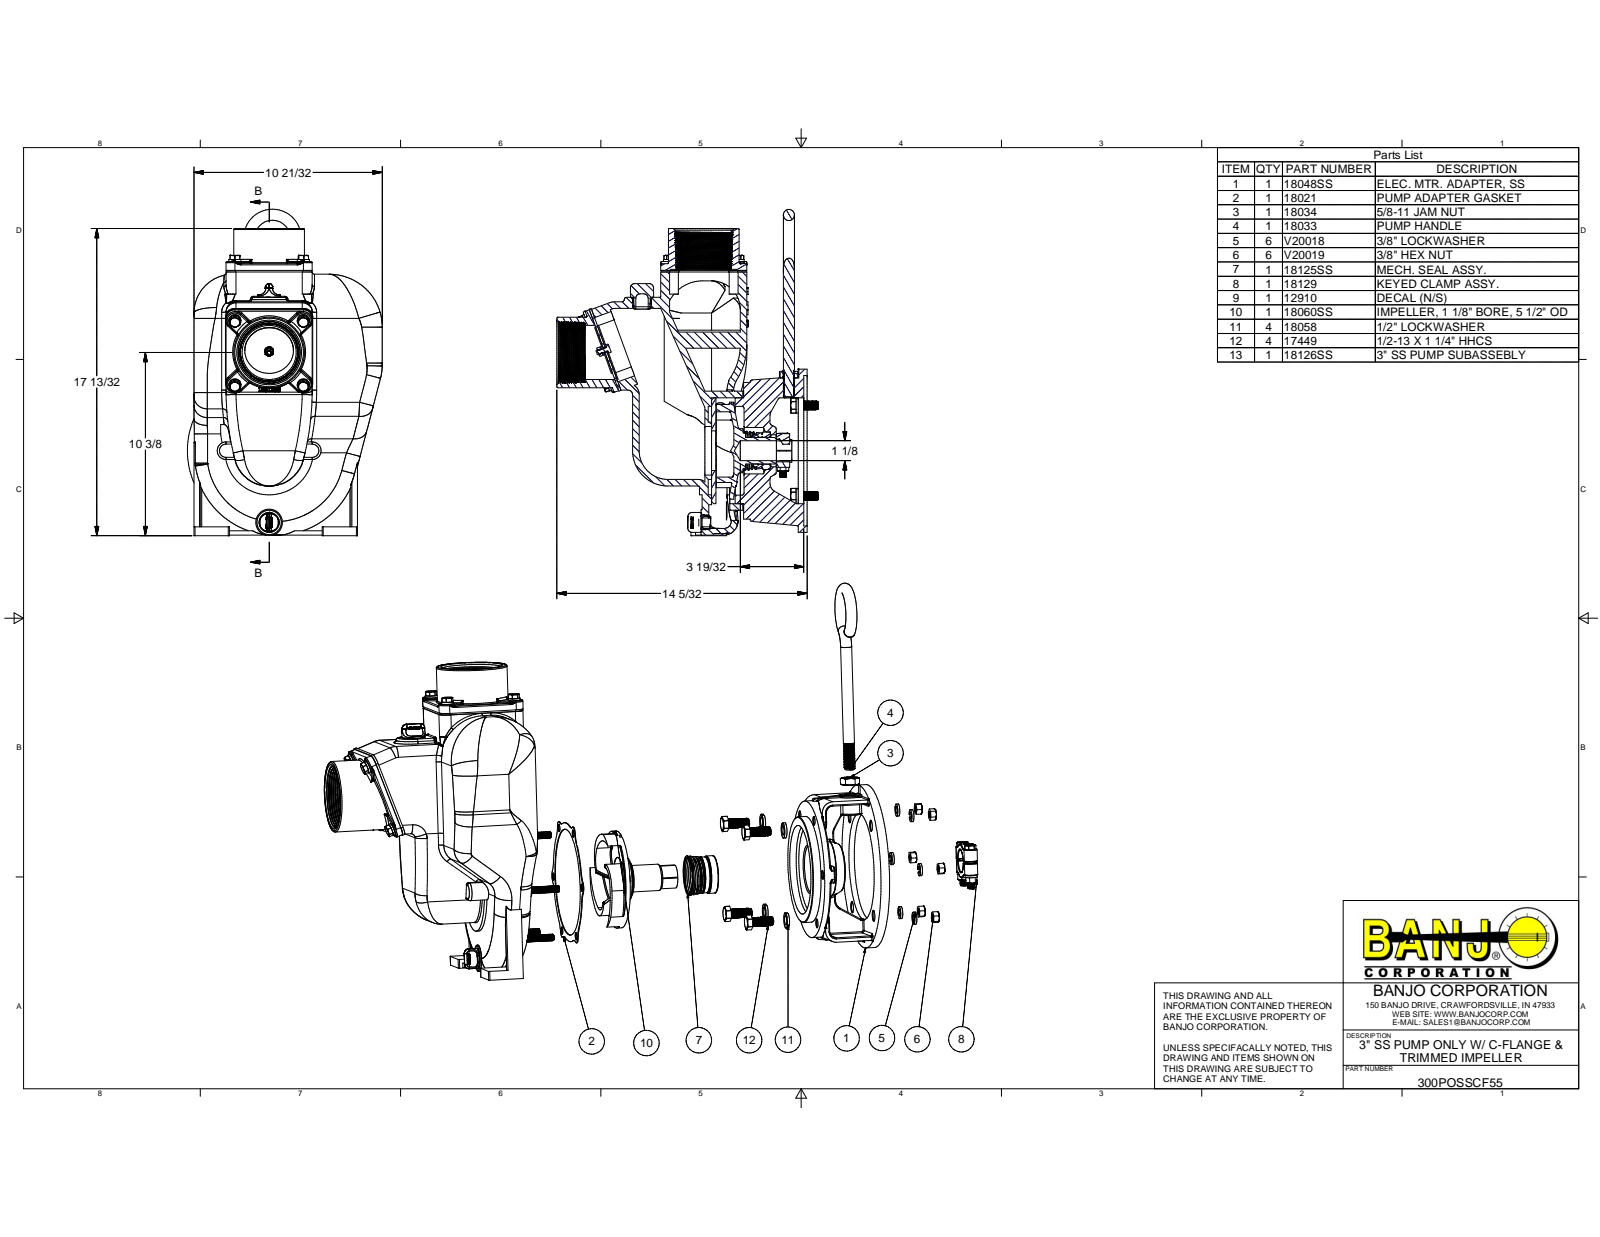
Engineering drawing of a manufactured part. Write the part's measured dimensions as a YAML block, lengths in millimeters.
part_name: "18001SS; 18004SS; 18106SS; V20018 (+8 more)"
step_written_by: "Autodesk Inventor 2014 (AUTOMOTIVE_DESIGN)"
units: millimeters
bodies: {solids: 73, faces: 6779, planar: 1336, cylindrical: 2286, other: 3157}
overall_size: [469.84, 375.46, 280.04]
volume: 5021000
surface_area: 1361000
round_holes:
  - {diameter: 10.32, count: 22}
  - {diameter: 7.8, count: 16}
  - {diameter: 9.78, count: 16}
  - {diameter: 7.81, count: 8}
  - {diameter: 9.52, count: 6}
  - {diameter: 11.11, count: 6}
  - {diameter: 13, count: 4}
  - {diameter: 14.29, count: 4}
  - {diameter: 13.92, count: 3}
  - {diameter: 7.14, count: 2}
  - {diameter: 12.7, count: 2}
  - {diameter: 4.98, count: 1}
round_bosses_or_shafts:
  - {diameter: 8.24, count: 196}
  - {diameter: 11.07, count: 60}
  - {diameter: 17.46, count: 16}
  - {diameter: 9.52, count: 12}
  - {diameter: 5.39, count: 12}
  - {diameter: 7.63, count: 6}
  - {diameter: 22.07, count: 4}
  - {diameter: 12.7, count: 4}
partial_cylinders:
  - {radius: 1.52, count: 98}
  - {radius: 12.7, count: 37}
  - {radius: 3.17, count: 33}
  - {radius: 0.76, count: 28}
  - {radius: 4.12, count: 24}
  - {radius: 6.35, count: 22}
  - {radius: 25.4, count: 22}
  - {radius: 9.53, count: 18}
face_to_face_distances: [9.52, 6.35, 9.53, 3.18, 7.94, 50.8, 124.68, 12.7, 55.53, 114.3]
hole_center_spacings: [98.42, 139.19, 69.6, 85.72, 98.43, 69.59, 24.05, 65.19]
